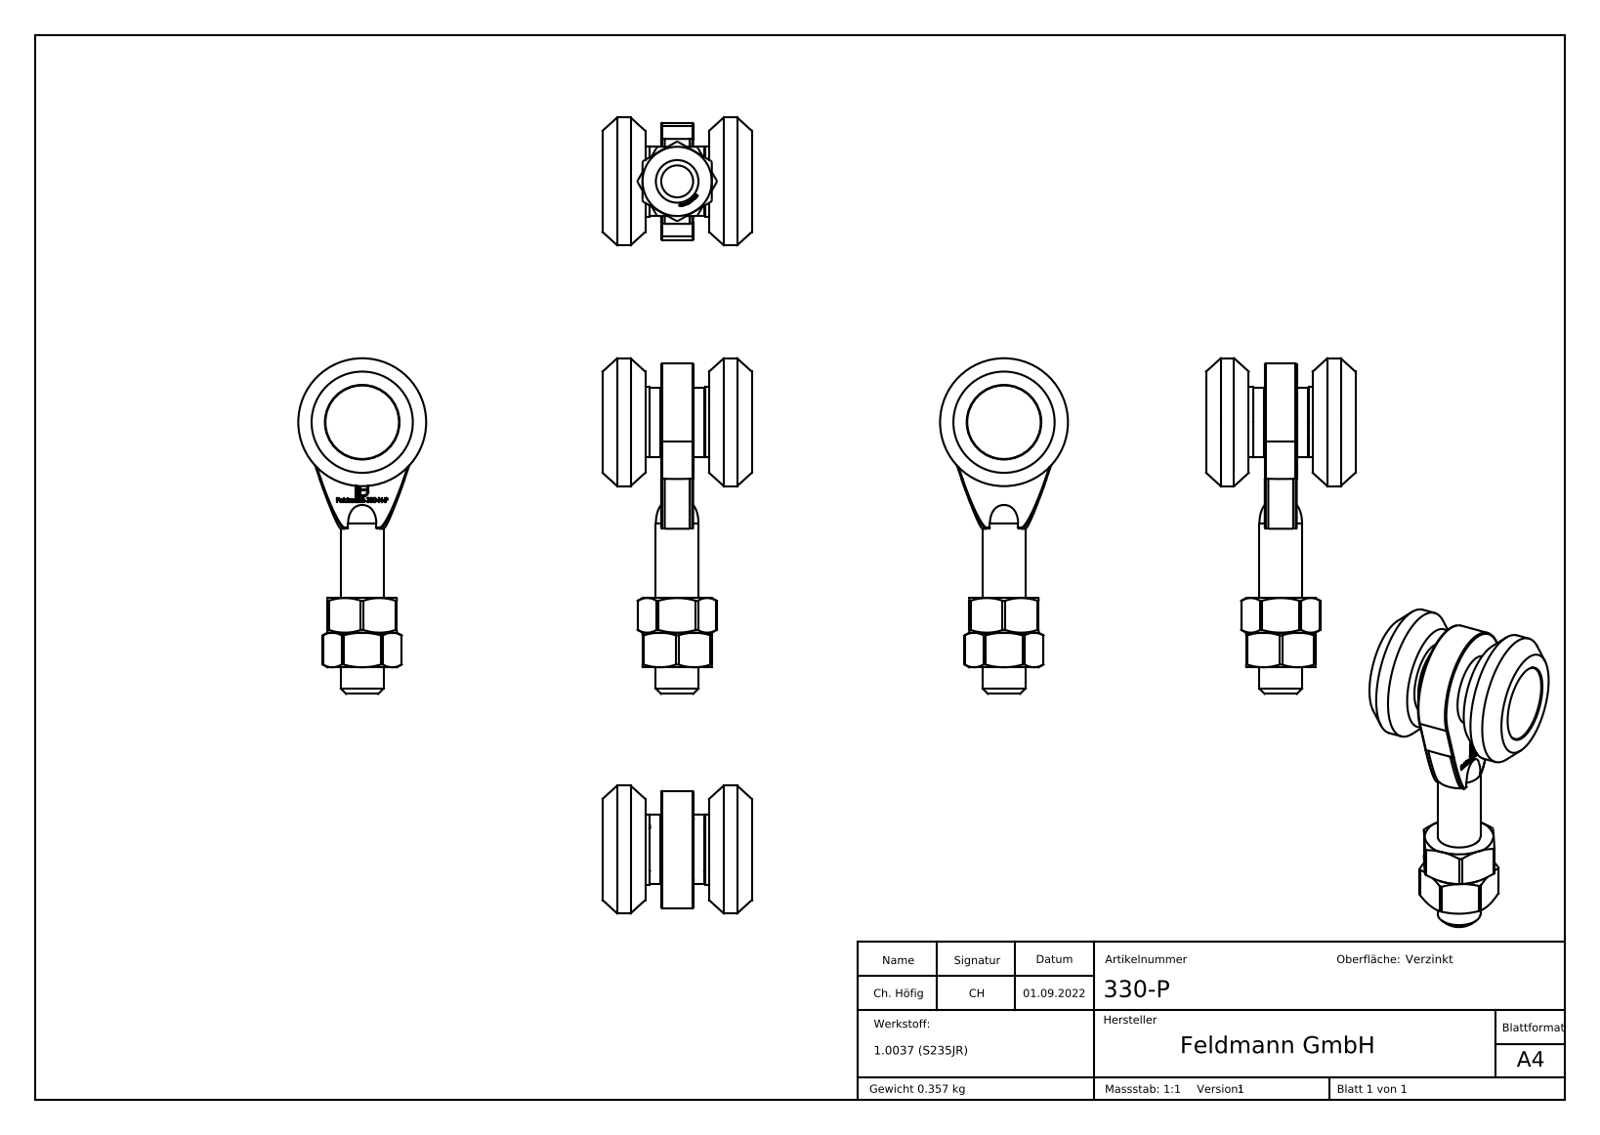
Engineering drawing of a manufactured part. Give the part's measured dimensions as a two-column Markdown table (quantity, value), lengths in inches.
| quantity | value |
| --- | --- |
| part name | DIN 934 M4-M20_DIN 934 M8; 330-P; 330-X-X Konfig_330-N-P Teil1 |
| STEP written by | SolidWorks 2018 (CONFIG_CONTROL_DESIGN) |
| units | inches |
| bodies | 7 solids, 818 faces (430 planar, 40 cylindrical, 348 other) |
| overall size | 2.48 × 1.102 × 0.945 |
| volume | 0.792 in³ |
| surface area | 12.38 in² |
| round holes (diameter × count) | 0.244 × 1, 0.268 × 1, 0.551 × 1 |
| round bosses / shafts (diameter × count) | 0.945 × 1, 0.543 × 1, 0.52 × 1, 0.512 × 1, 0.315 × 1, 0.24 × 1 |
| partial cylindrical surfaces (radius × count) | 0.02 × 12, 0.008 × 6, 0.433 × 1 |
| main face-to-face distances | 0.307, 0.315, 0.748, 0.031, 0.394, 0.035, 0.752, 0.634, 0.236, 0.311 |
